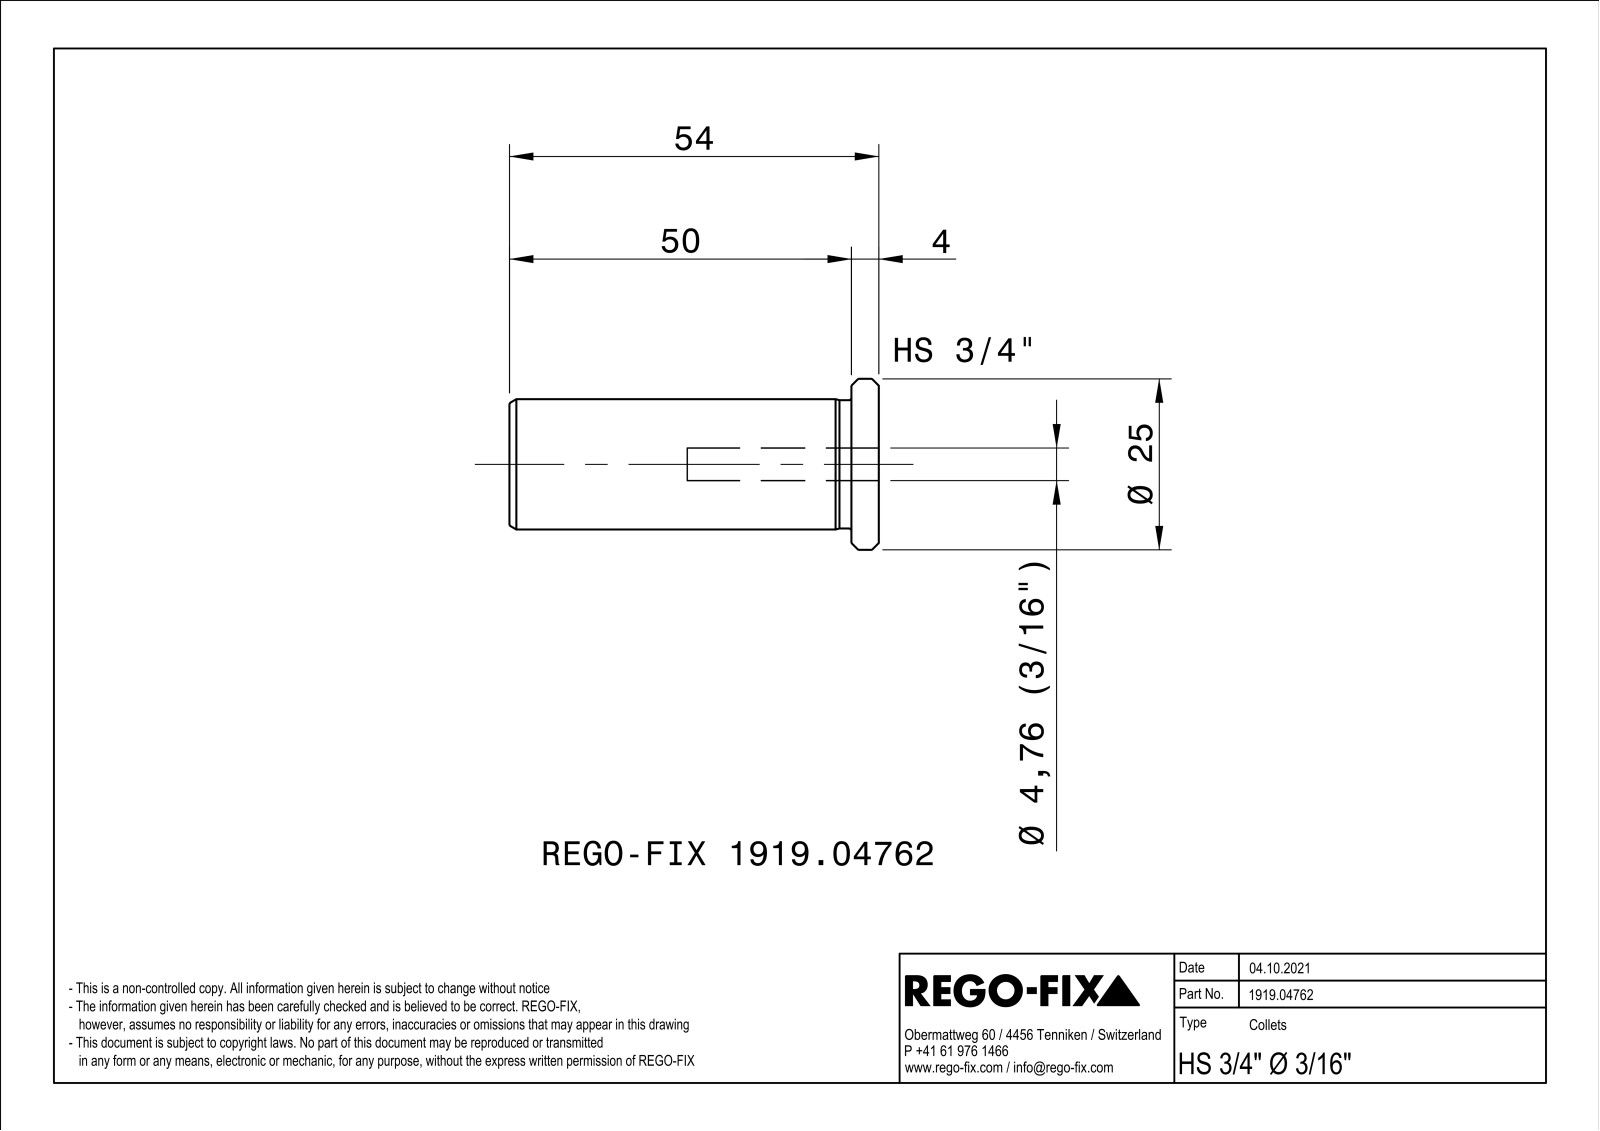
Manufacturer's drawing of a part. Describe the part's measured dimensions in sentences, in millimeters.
The part is named "NOCUT". Its 3-D file was written by "SIEMENS PLM Software Solid Edge ST10 (AUTOMOTIVE_DESIGN)". It is 1 solid with 75 faces: 22 planar, 12 cylindrical and 41 other. Overall it measures 54 by 24.98 by 24.98 millimeters. Its volume is 11 205 cubic millimeters and its surface area 7 217 square millimeters. Round holes: 1 of diameter 4.76, 1 of diameter 10, 1 of diameter 16.5. Round bosses or shafts: 1 of diameter 25, 1 of diameter 19.05, 1 of diameter 18.75. The main face-to-face distances are 1, 4, 54, 50.
